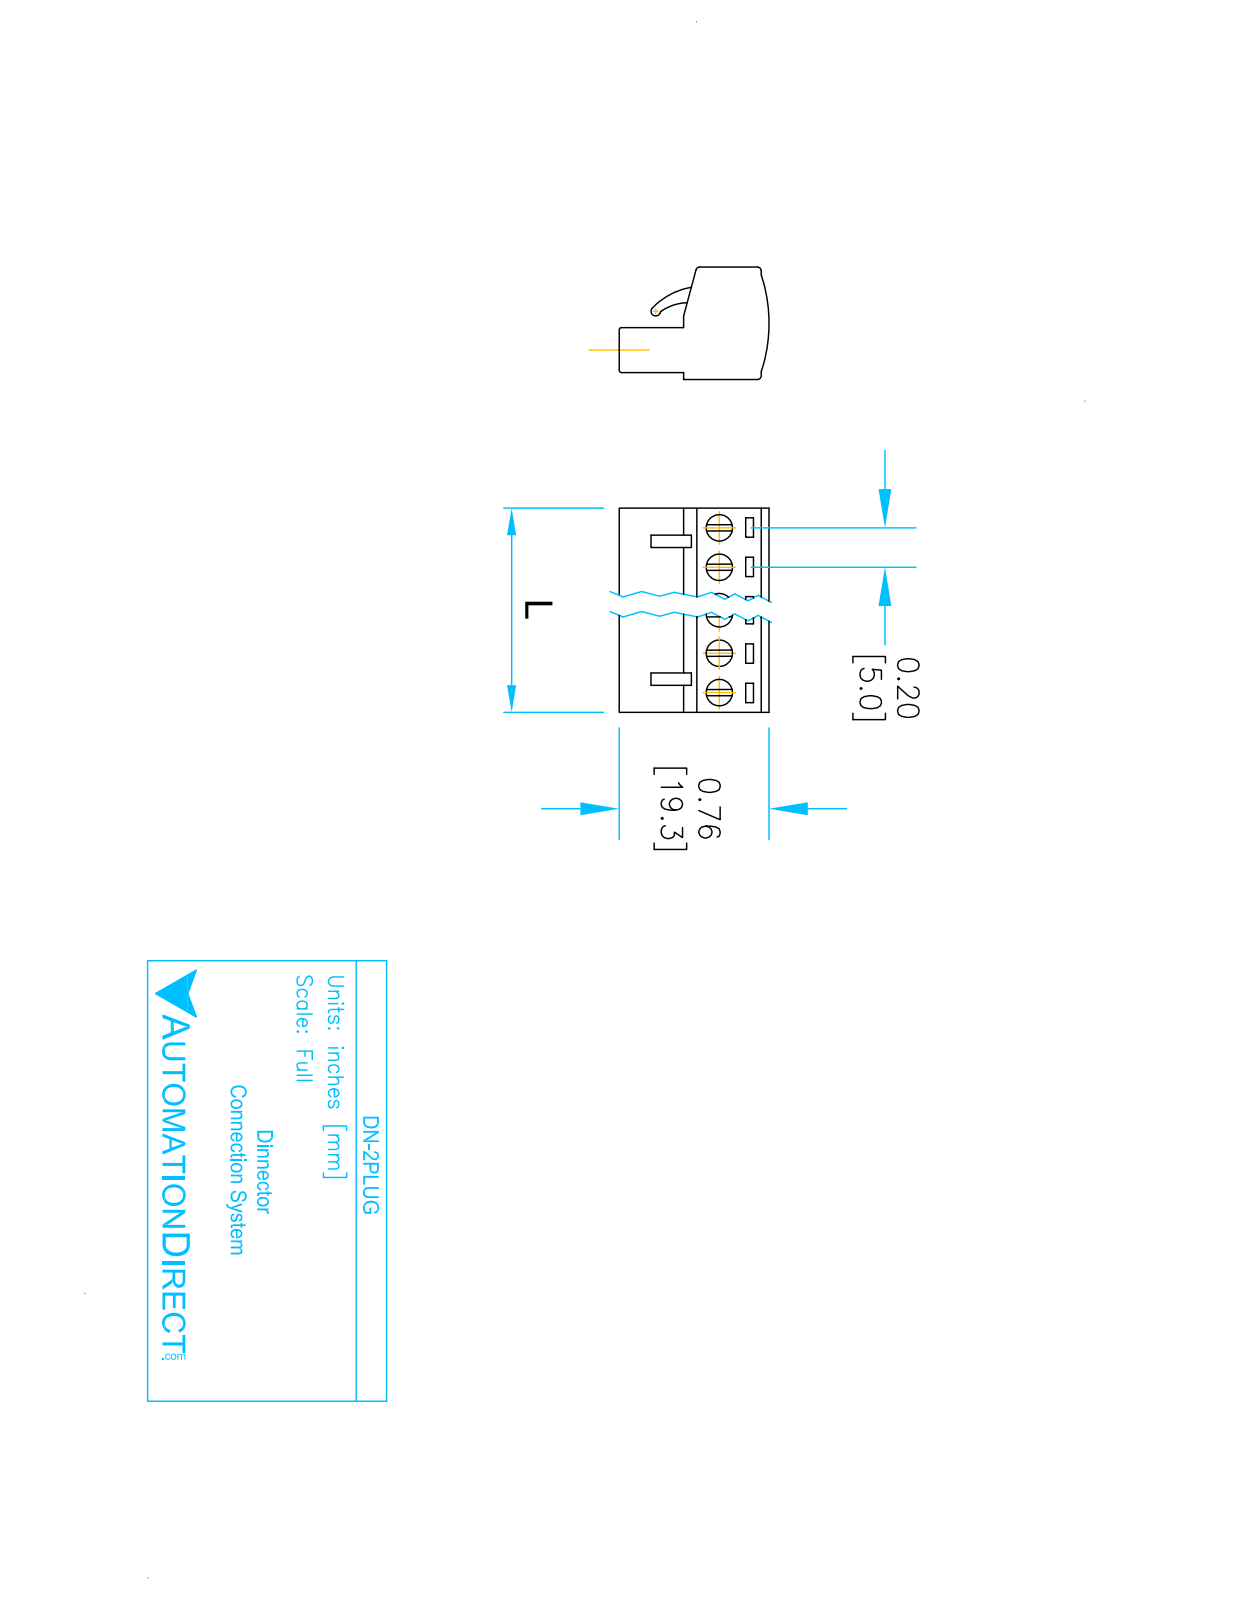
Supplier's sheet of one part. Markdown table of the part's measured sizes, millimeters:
| quantity | value |
| --- | --- |
| part name | 49002_S |
| STEP written by | SolidWorks 2013 (AUTOMOTIVE_DESIGN) |
| units | millimeters |
| bodies | 1 solid, 164 faces (113 planar, 41 cylindrical, 10 other) |
| overall size | 19.3 × 14.5 × 10.16 |
| volume | 1 743 mm³ |
| surface area | 1 517 mm² |
| round holes (diameter × count) | 1.6 × 2, 2.5 × 2, 3.4 × 2, 3.6 × 2 |
| round bosses / shafts (diameter × count) | 3 × 2 |
| partial cylindrical surfaces (radius × count) | 0.5 × 3, 0.3 × 2, 2.9 × 2, 0.6 × 1, 6 × 1, 9 × 1, 20.03 × 1 |
| main face-to-face distances | 10.16, 6.7, 1, 5.08, 14.5, 7.8, 3.4, 0.79, 4.29, 0.89 |
| hole center spacings | 5.08 |
